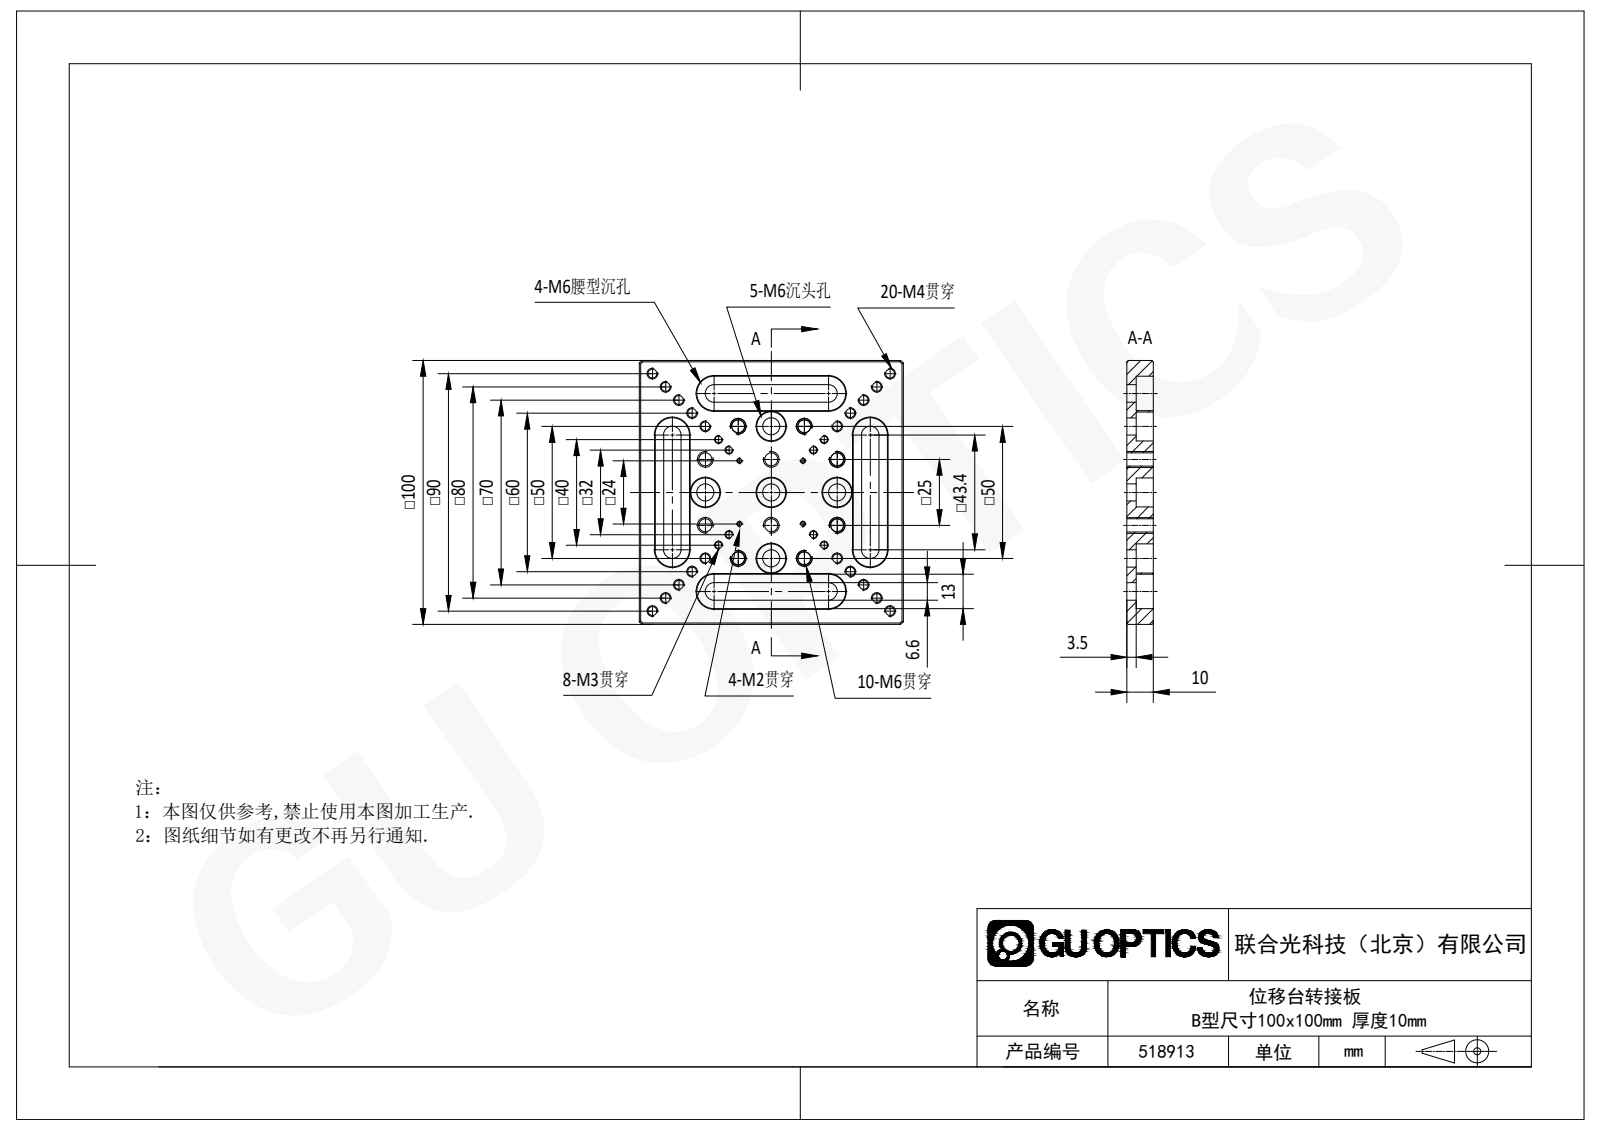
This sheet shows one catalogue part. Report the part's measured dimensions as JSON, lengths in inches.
{"step_written_by": "SolidWorks 2020 (CONFIG_CONTROL_DESIGN)", "units": "inches", "bodies": {"solids": 1, "faces": 182, "planar": 59, "cylindrical": 68, "other": 55}, "overall_size": [3.937, 3.937, 0.394], "volume_in3": 4.235, "surface_area_in2": 47.42, "round_holes": [[0.13, 20], [0.197, 10], [0.098, 8], [0.256, 5], [0.433, 5], [0.063, 4]], "partial_cylinders_radius": [[0.13, 8], [0.256, 8]], "face_to_face_distances": [0.394, 0.138, 0.256, 3.937, 2.953, 0.126, 0.386, 0.236, 0.748, 3.189], "hole_center_spacings": [0.278, 1.113, 2.06, 0.984, 0.557, 0.696, 0.723, 1.433]}
